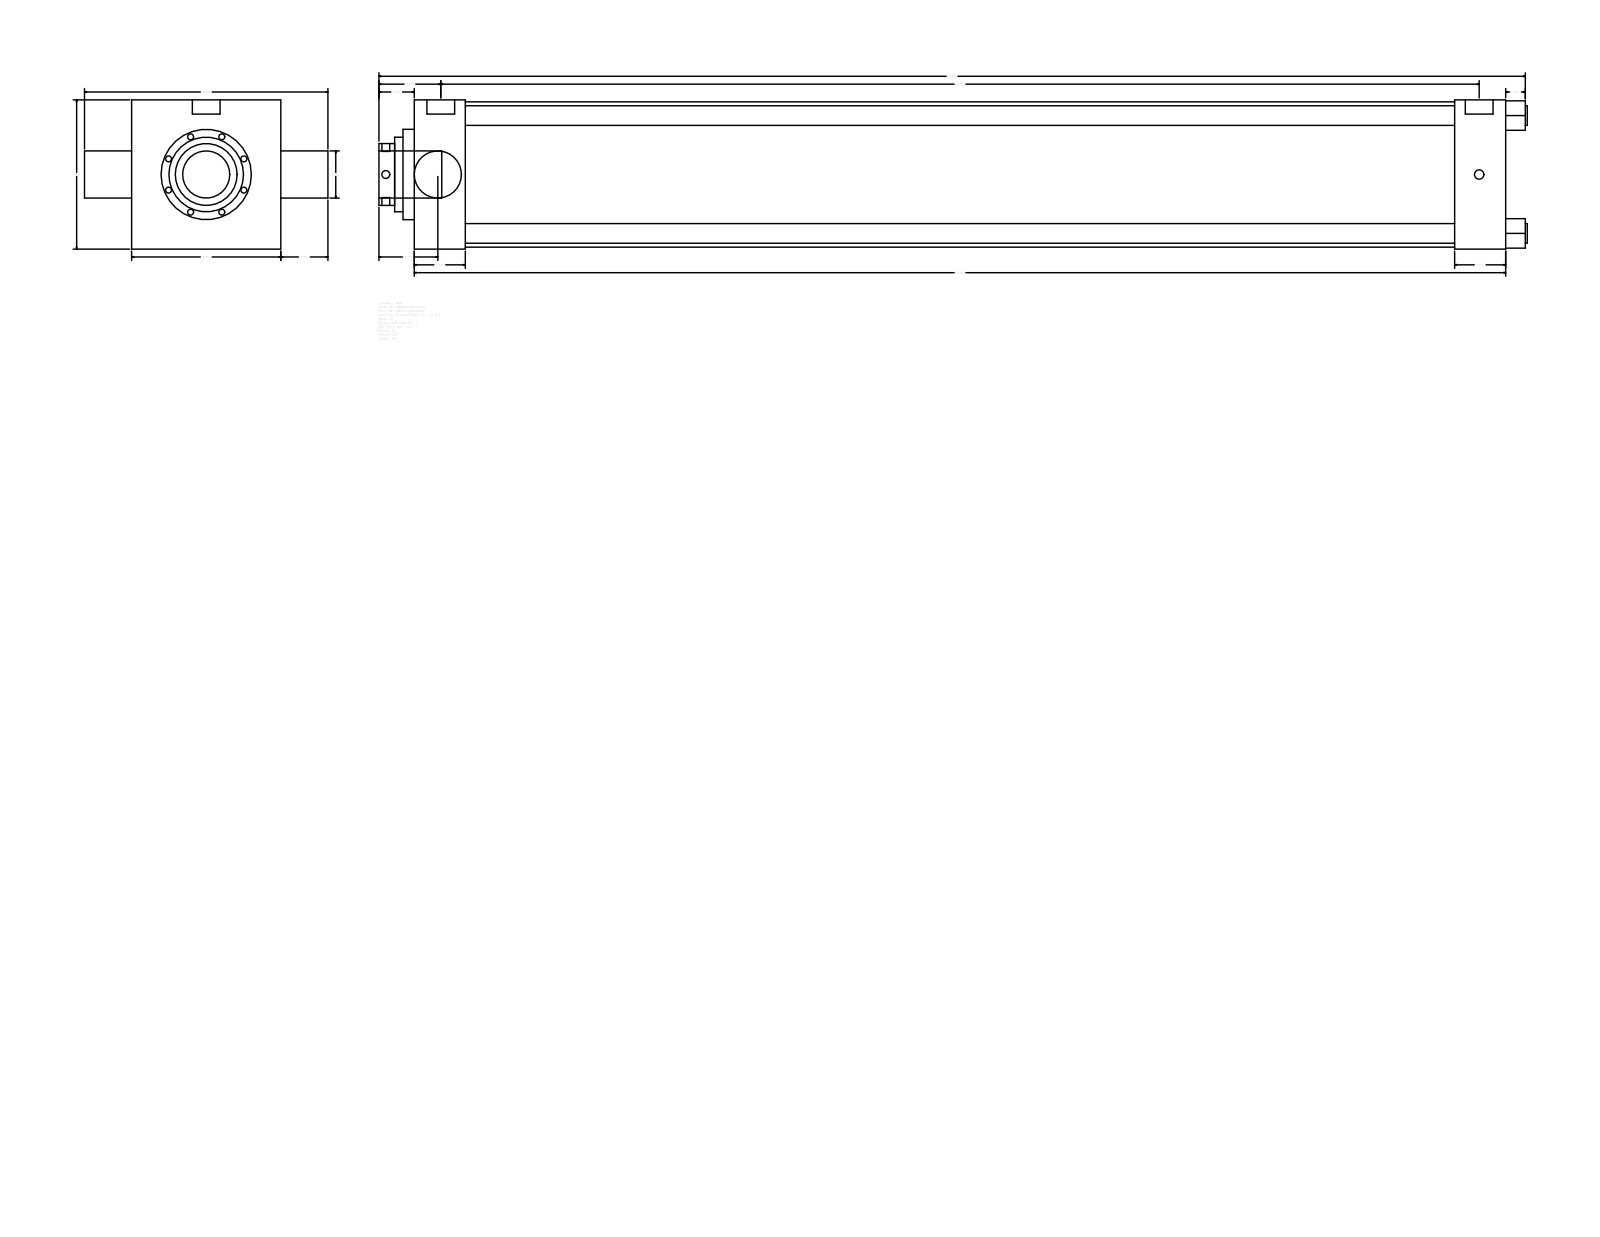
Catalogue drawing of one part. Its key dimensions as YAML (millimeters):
part_name: "HH_TF__0800_4"
step_written_by: "GSSL Pune (CONFIG_CONTROL_DESIGN)"
units: millimeters
bodies: {solids: 0, faces: 93, planar: 68, cylindrical: 25, other: 0}
overall_size: [1857.38, 393.7, 241.3]
round_holes:
  - {diameter: 31.75, count: 4}
  - {diameter: 76.2, count: 1}
  - {diameter: 101.6, count: 1}
  - {diameter: 120.65, count: 1}
  - {diameter: 146.05, count: 1}
  - {diameter: 234.95, count: 1}
round_bosses_or_shafts:
  - {diameter: 15.08, count: 3}
  - {diameter: 44.86, count: 2}
  - {diameter: 12.7, count: 2}
  - {diameter: 76.2, count: 1}
face_to_face_distances: [241.3, 1765.3, 82.55, 1682.75, 76.2, 1600.2, 317.5, 31.75, 114.3, 1714.5]
hole_center_spacings: [134.7, 190.5, 269.41]
